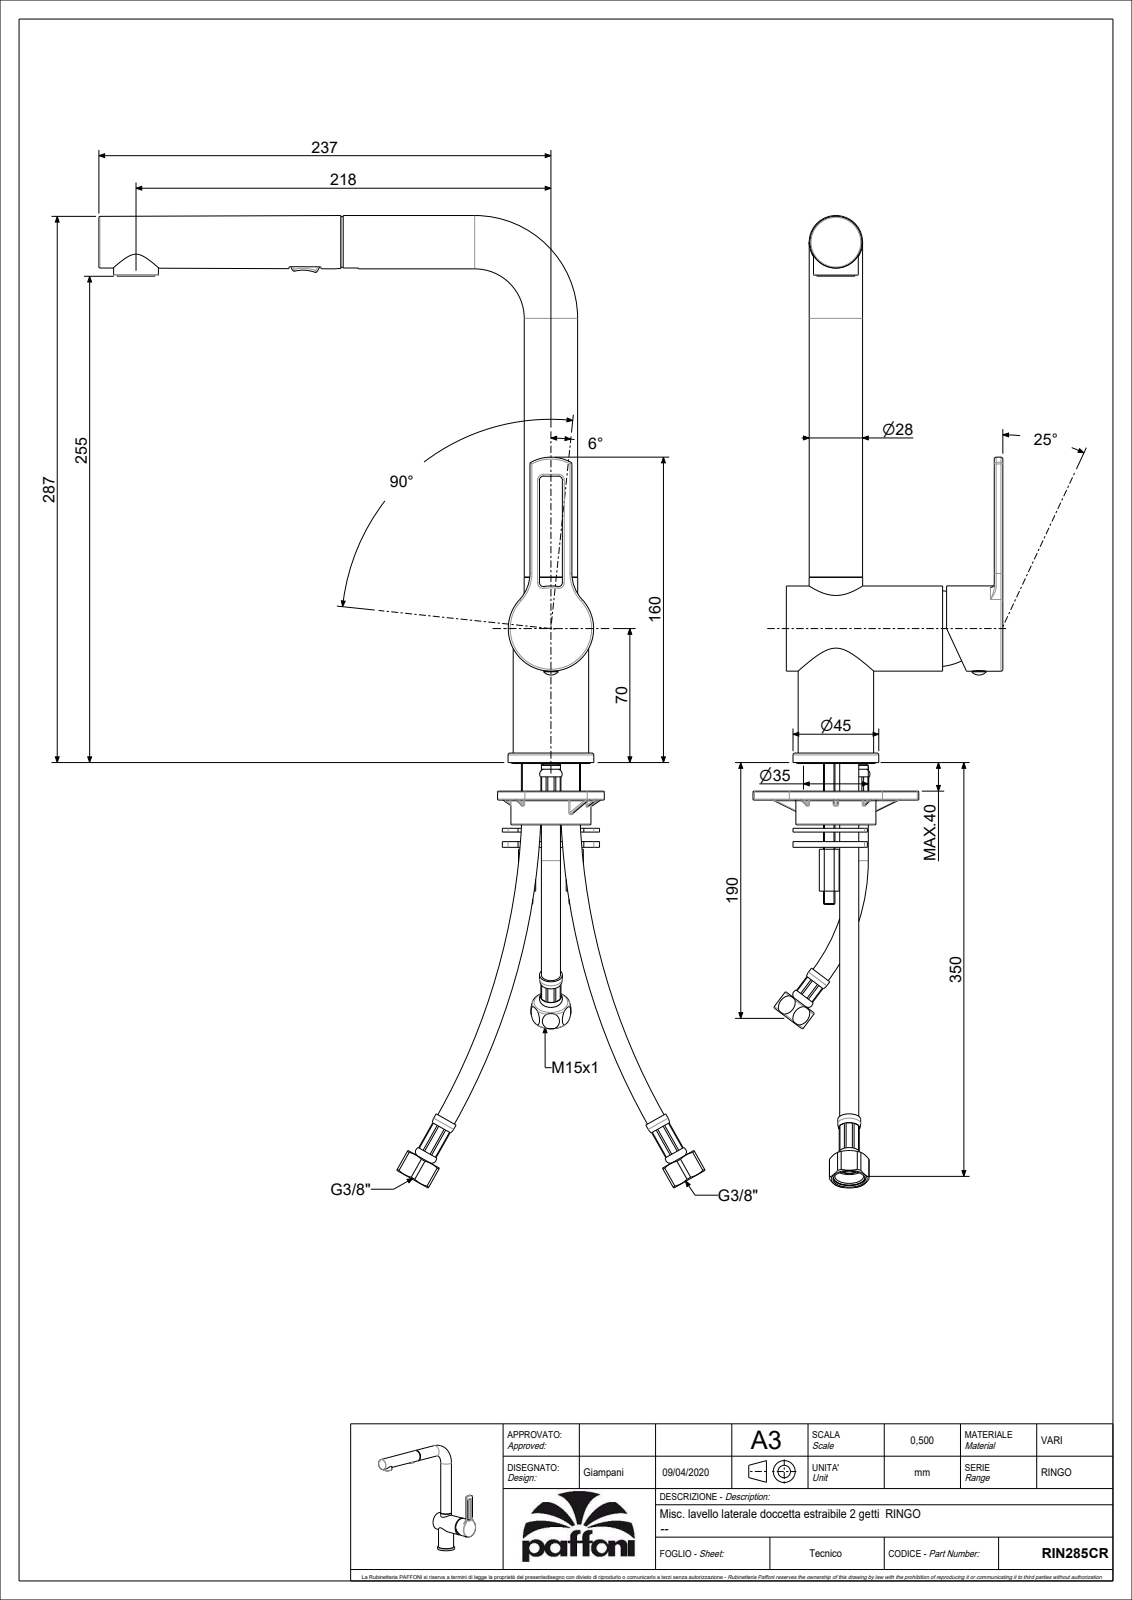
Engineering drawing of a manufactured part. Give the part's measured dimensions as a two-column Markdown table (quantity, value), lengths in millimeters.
| quantity | value |
| --- | --- |
| part name | RIN285CR |
| STEP written by | CREO PARAMETRIC BY PTC INC, 2020044 (CONFIG_CONTROL_DESIGN) |
| units | millimeters |
| bodies | 2 solids, 2417 faces (1202 planar, 622 cylindrical, 593 other) |
| overall size | 287.4 × 260.5 × 113.63 |
| volume | 207 539 mm³ |
| surface area | 156 342 mm² |
| round holes (diameter × count) | 6.5 × 3, 7 × 3, 8.6 × 3, 9.4 × 3, 5.5 × 2, 25 × 2, 36 × 2, 3 × 1, 3.4 × 1, 3.5 × 1, 4 × 1, 4.6 × 1 |
| round bosses / shafts (diameter × count) | 28 × 2, 21 × 2, 20 × 2, 45 × 1, 44.8 × 1, 44.7 × 1, 39.6 × 1, 38.5 × 1 |
| partial cylindrical surfaces (radius × count) | 0.5 × 62, 0.2 × 42, 0.3 × 25, 1 × 22, 24.3 × 12, 1.7 × 6, 2 × 6, 1.5 × 5 |
| main face-to-face distances | 3.5, 1.5, 2, 70.8, 5, 15.5, 3, 15, 11.2, 21 |
| hole center spacings | 10.79, 11.18, 12.21, 12.98, 19.91, 24.83, 4.75, 10.01 |
